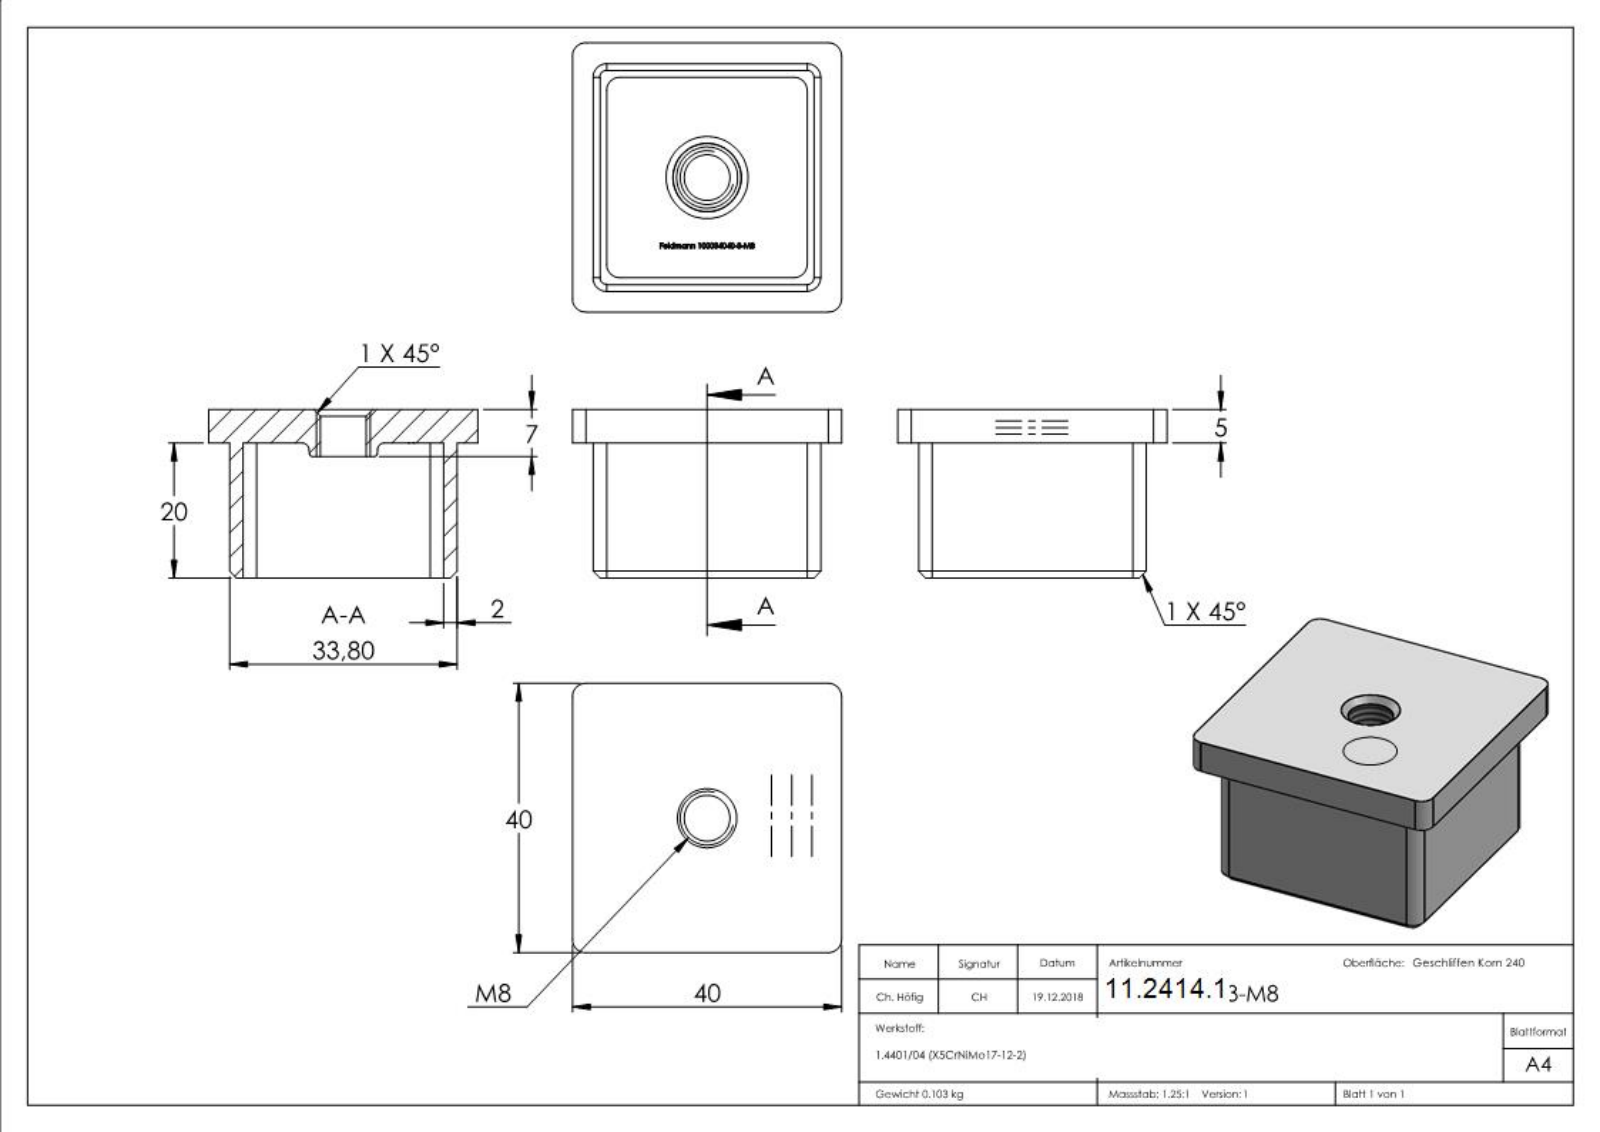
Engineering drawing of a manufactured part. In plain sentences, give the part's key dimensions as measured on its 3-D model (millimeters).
The part is named "100034040-3-M8". Its 3-D file was written by "SolidWorks 2015 (CONFIG_CONTROL_DESIGN)". It is 1 solid with 332 faces: 168 planar, 14 cylindrical and 150 other. Overall it measures 40 by 40 by 25 millimeters. Its volume is 12 907 cubic millimeters and its surface area 8 963 square millimeters. Round holes: 1 of diameter 6.8. Partial cylindrical surfaces (rounded edges, fillets, slot ends): 12 of radius 2. The main face-to-face distances are 2, 31.8, 5, 33.8, 29.8, 5.1, 3.1, 34.9, 36.9, 40.
